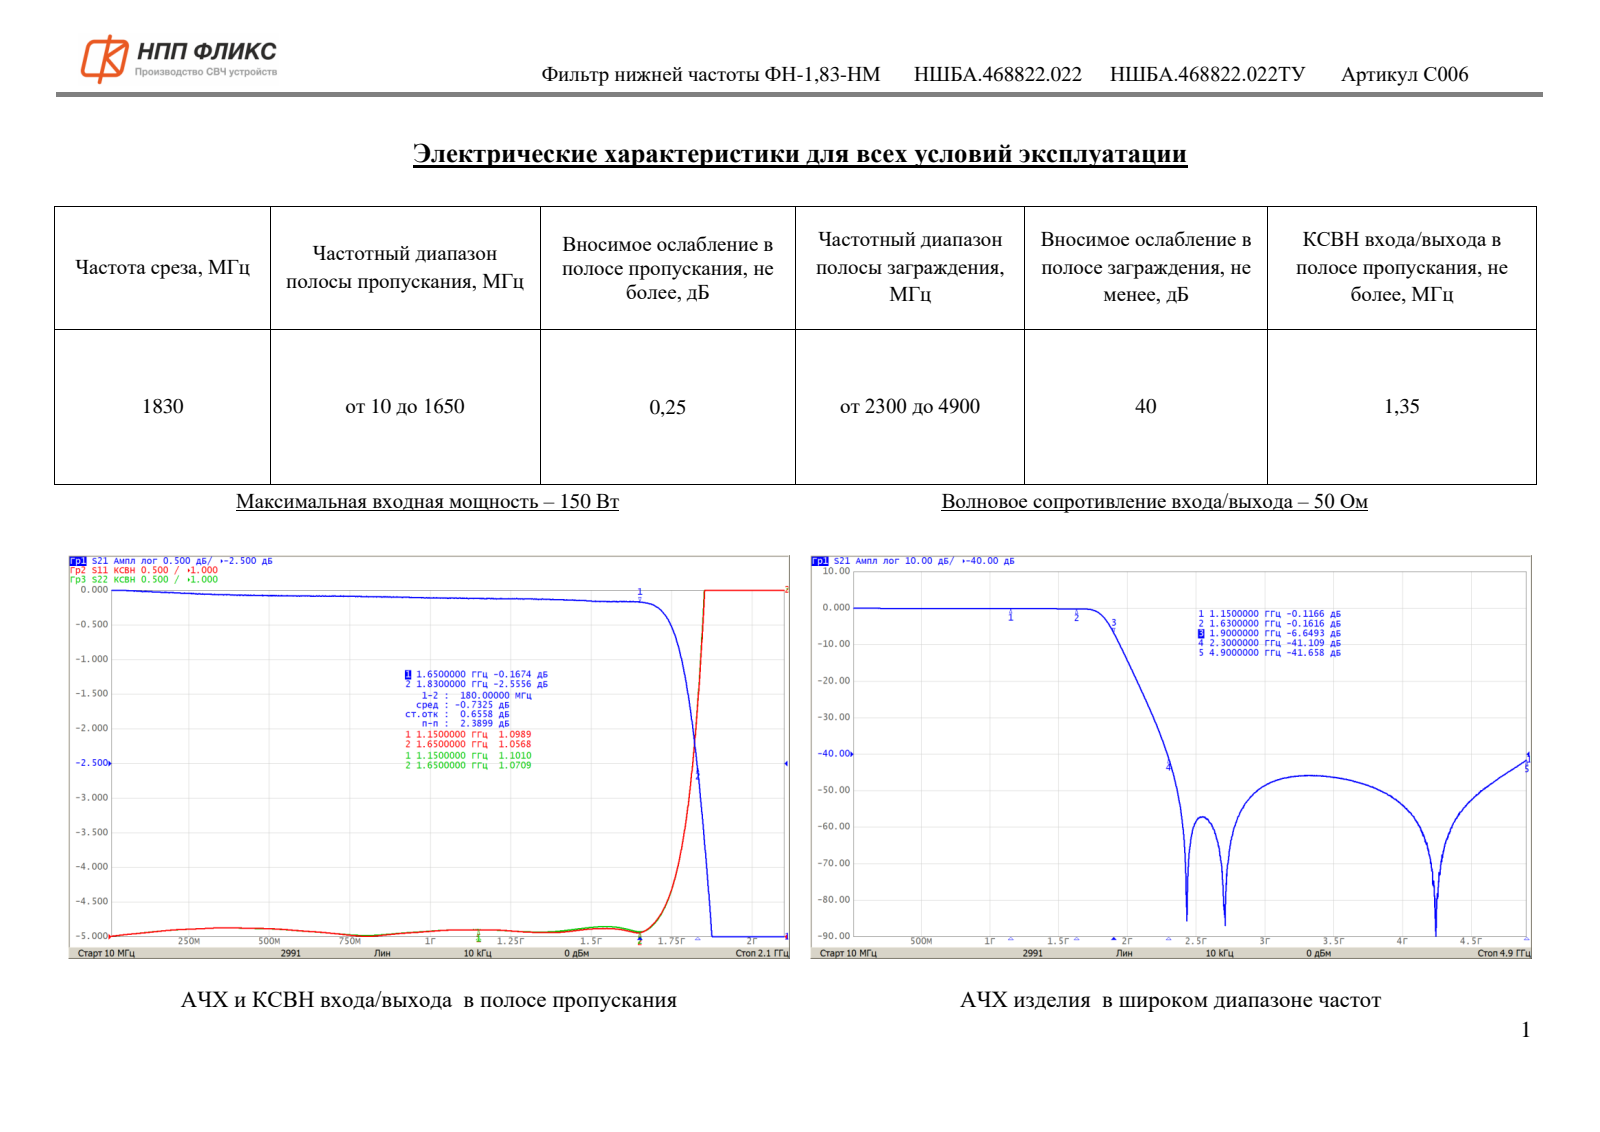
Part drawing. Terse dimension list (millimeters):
name: НШБА.468822.022_Фильтр ФН-1,83-НМ
written by: ASCON Math Kernel (CONFIG_CONTROL_DESIGN)
unit: mm
bodies: 10 solids, 617 faces (406 planar, 105 cylindrical, 106 other)
size: 80.6 × 30.7 × 20.85
volume: 21 903 mm³; area: 10 391 mm²
holes: 6× ⌀3.3, 4× ⌀3.2, 3× ⌀2.5, 1× ⌀4.1, 1× ⌀8.3
bosses: 4× ⌀6, 4× ⌀5.6, 4× ⌀3, 1× ⌀15.7, 1× ⌀13.8, 1× ⌀10.4, 1× ⌀4, 1× ⌀2.9
rounds: 24× R2, 4× R0.5, 4× R1, 3× R0.6, 1× R0.3, 1× R0.9, 1× R1.05
face distances: 19.6, 18.7, 0.6, 20.2, 0.5, 47.5, 47, 2.5, 45.5, 2
hole spacings: 8.98, 12.7, 17.96, 24.7, 37, 44.49
